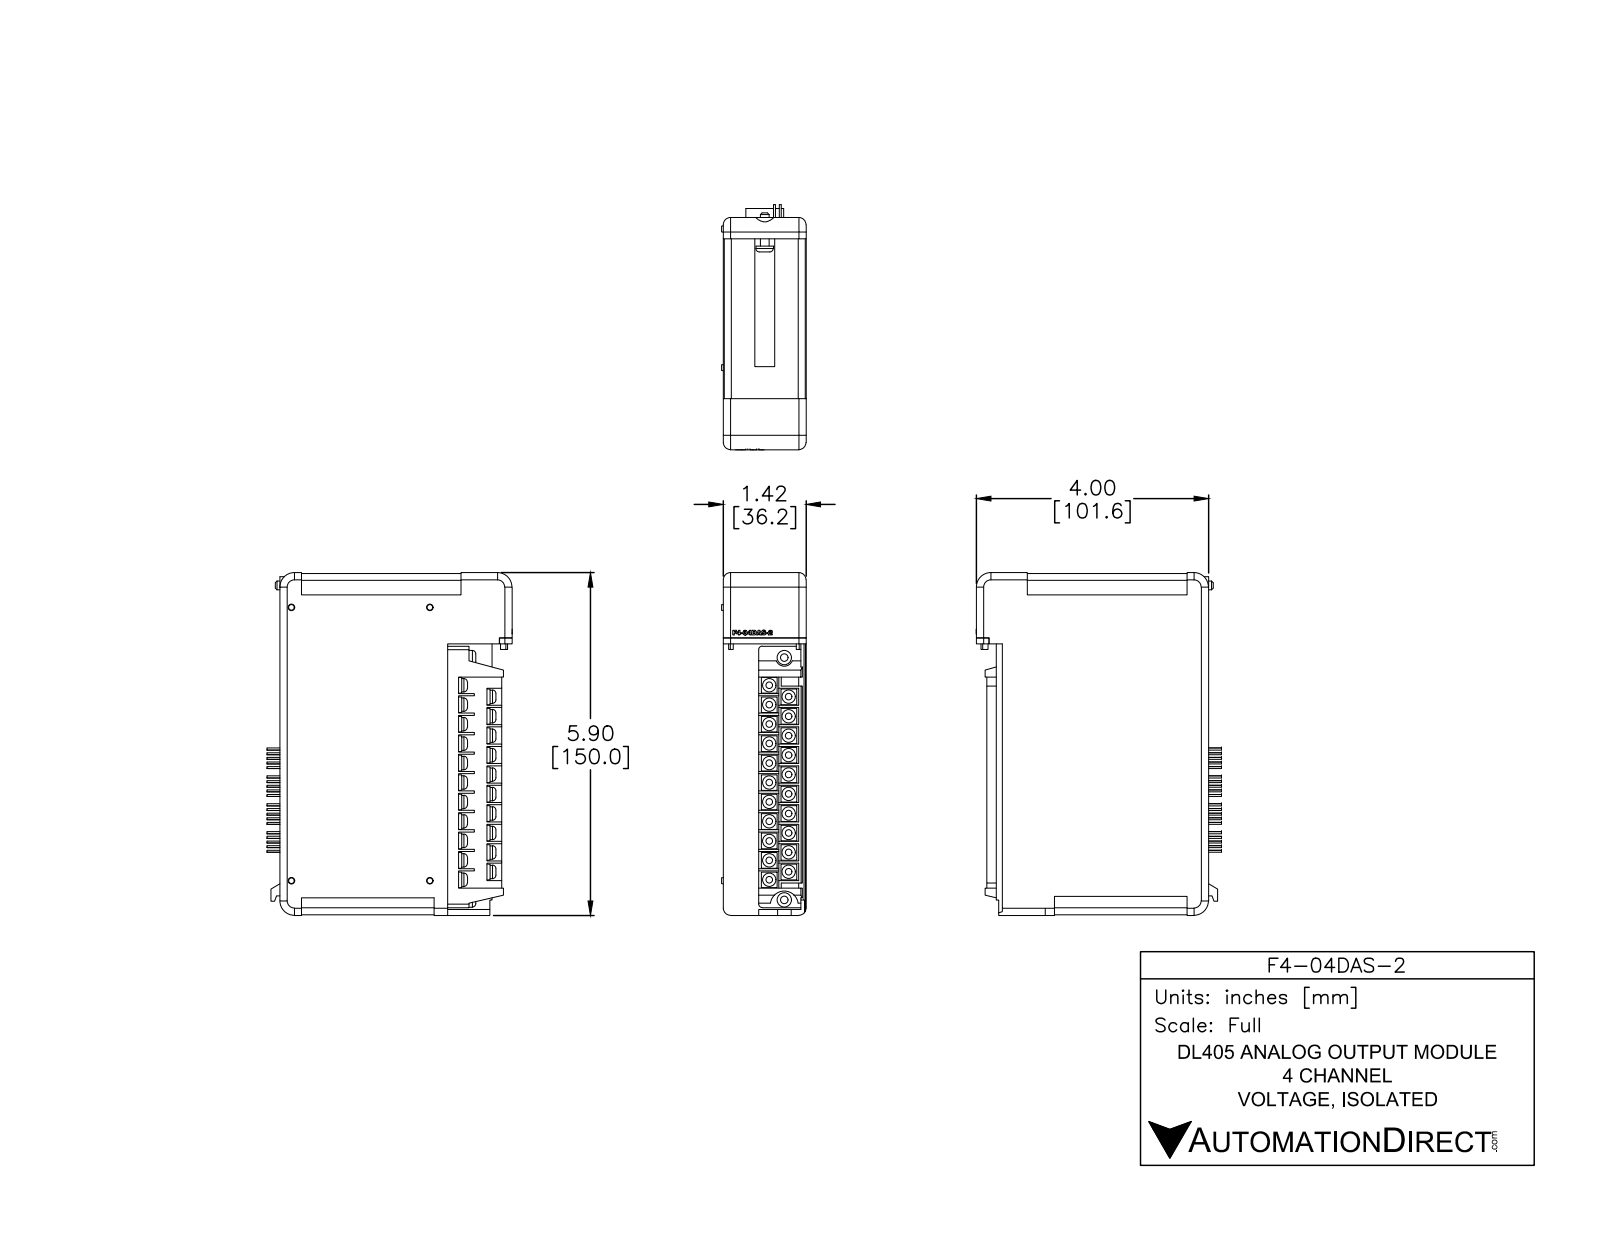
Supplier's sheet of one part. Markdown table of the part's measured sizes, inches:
| quantity | value |
| --- | --- |
| part name | F4-04DAS-2 |
| STEP written by | SolidWorks 2014 (AUTOMOTIVE_DESIGN) |
| units | inches |
| bodies | 6 solids, 924 faces (571 planar, 246 cylindrical, 107 other) |
| overall size | 5.905 × 4.223 × 1.455 |
| volume | 27.6 in³ |
| surface area | 90.48 in² |
| round bosses / shafts (diameter × count) | 0.23 × 21, 0.035 × 20, 0.035 × 20, 0.25 × 2, 0.3 × 1, 0.15 × 1 |
| partial cylindrical surfaces (radius × count) | 0.015 × 82, 0.125 × 8, 0.12 × 4, 0.25 × 3, 0.03 × 2, 0.06 × 2, 0.149 × 1, 0.151 × 1 |
| main face-to-face distances | 1.425, 0.015, 2.89, 5.875, 1.41, 0.47, 0.955, 5.89, 1.21, 0.345 |
